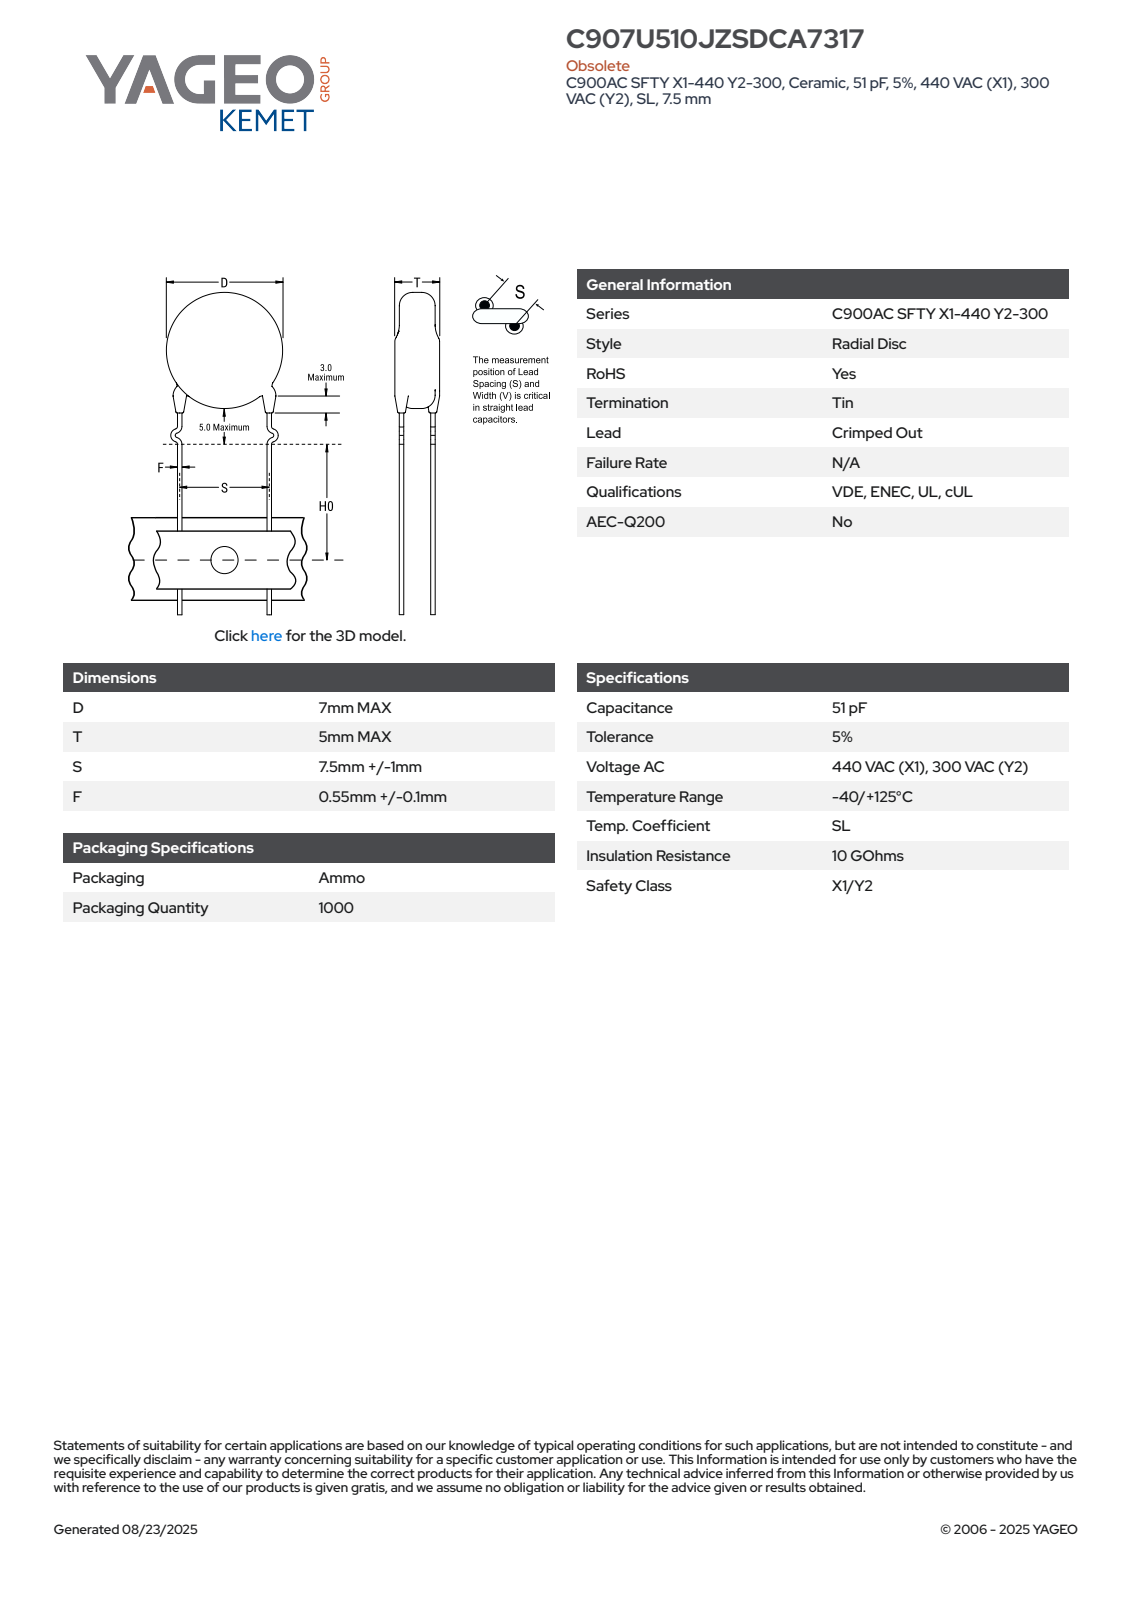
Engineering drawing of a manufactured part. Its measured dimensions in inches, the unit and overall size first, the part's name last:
Units: inches
Overall size (bounding box): 1.26 × 0.466 × 0.215
Round bosses / shafts (diameter × count): ⌀0.047 ×2, ⌀0.276 ×1
Main face-to-face distances: 0.197, 0.029, 0.152, 0.124, 0.023, 0.013, 0.117, 0.059, 0.085, 0.088
Volume: 0.013 in³ · Surface area: 0.462 in²
Bodies: 4 solids, 87 faces (63 planar, 6 cylindrical, 18 other)
Part name (STEP PRODUCT): CCD_KCOC900_D7T5S7.5LL20F0.55
STEP written by: SolidWorks 2014 (AUTOMOTIVE_DESIGN)
